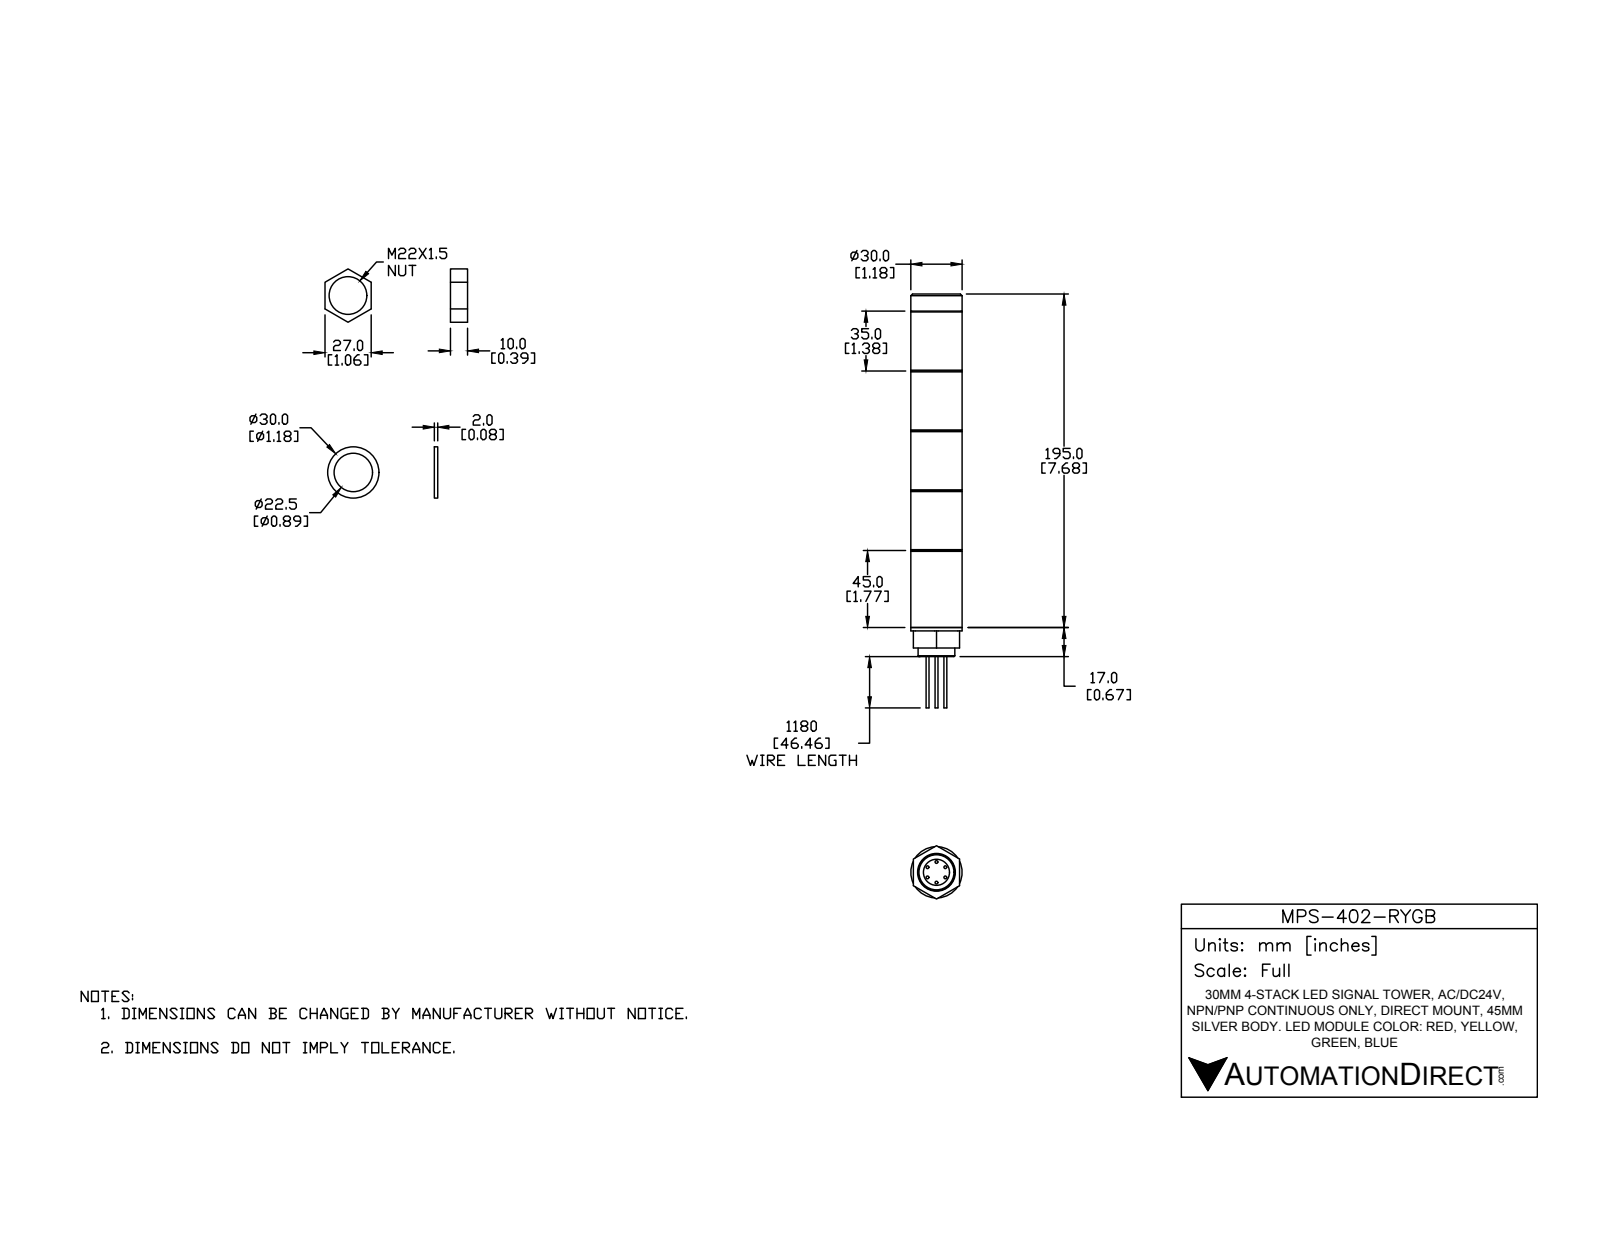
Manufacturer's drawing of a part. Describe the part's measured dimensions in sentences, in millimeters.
The part is named "MPS-402-RYGB". Its 3-D file was written by "SolidWorks 2016 (AUTOMOTIVE_DESIGN)". It is 15 solids with 119 faces: 53 planar, 42 cylindrical and 24 other. Overall it measures 242 by 31.18 by 30 millimeters. Its volume is 133 764 cubic millimeters and its surface area 36 910 square millimeters. Round holes: 1 of diameter 3.2, 1 of diameter 7.7, 1 of diameter 15.3, 1 of diameter 20.7, 1 of diameter 22. Round bosses or shafts: 6 of diameter 1.7, 1 of diameter 30, 1 of diameter 21.5, 1 of diameter 5. The main face-to-face distances are 35, 70, 105, 45, 80, 115, 150, 140, 47, 82.
